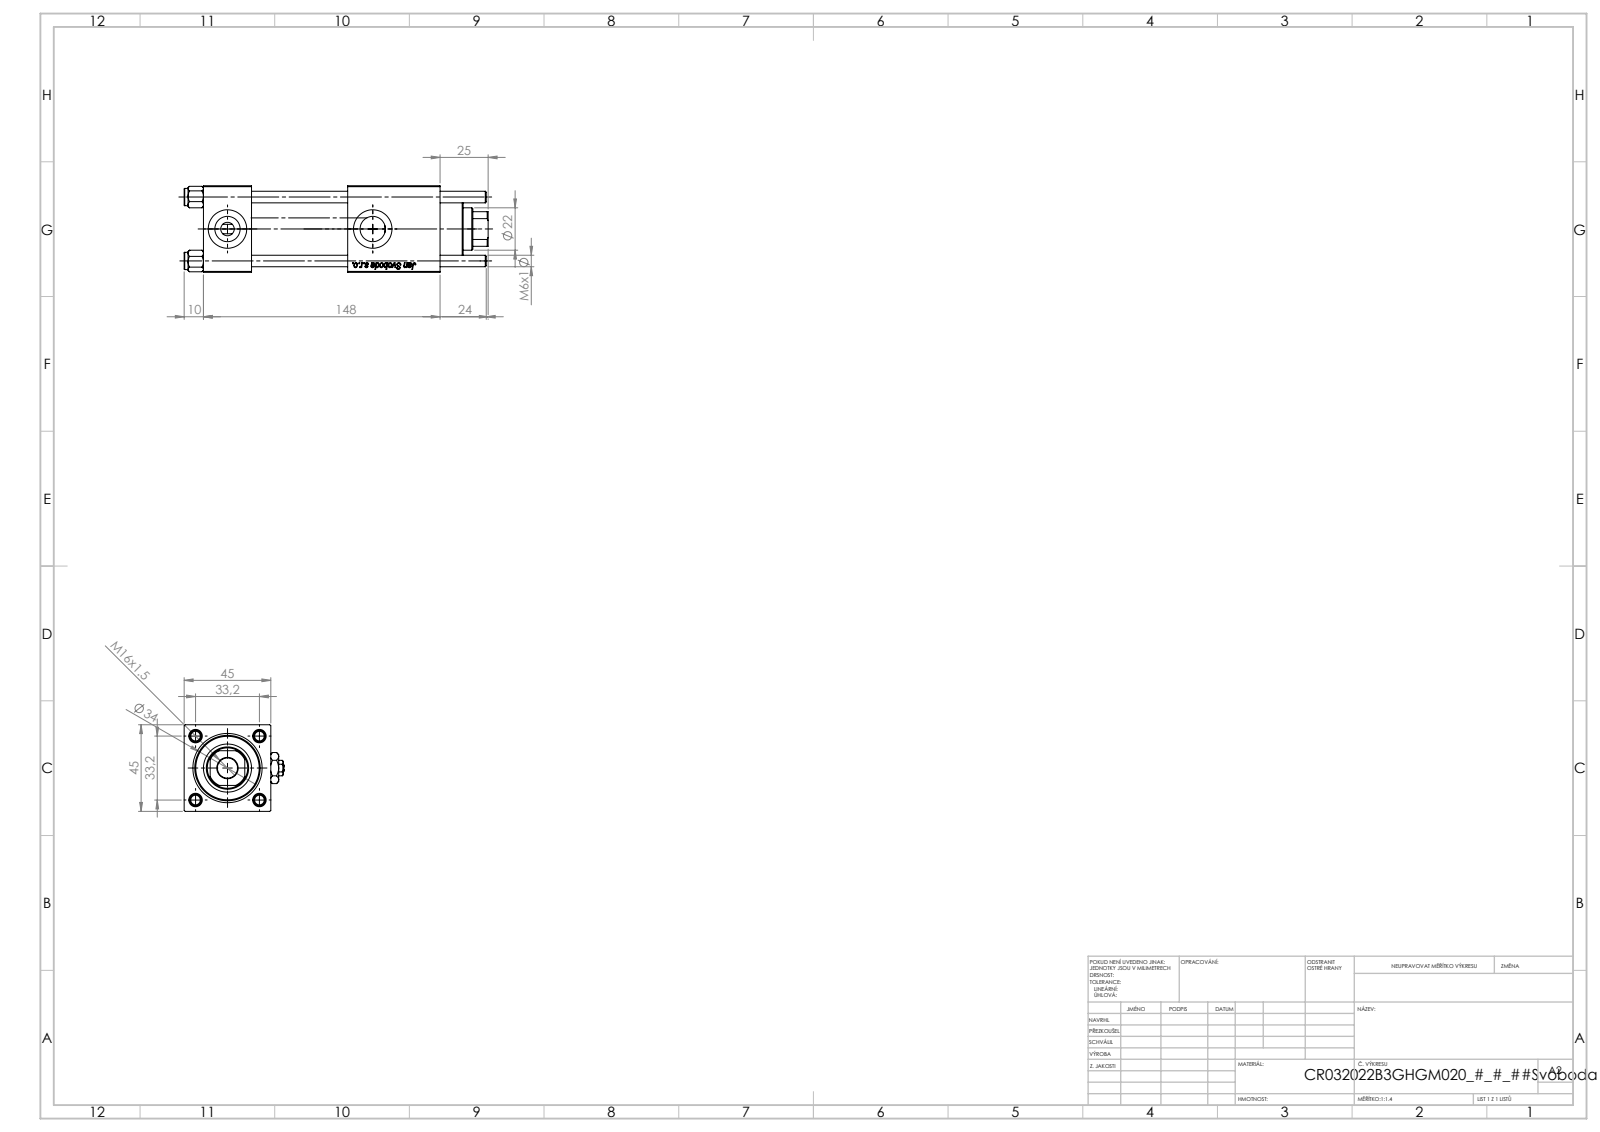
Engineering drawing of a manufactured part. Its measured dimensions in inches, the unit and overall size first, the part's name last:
Units: inches
Overall size (bounding box): 6.22 × 2.047 × 1.772
Round holes (diameter × count): ⌀0.236 ×4, ⌀0.276 ×2, ⌀0.518 ×2, ⌀0.787 ×2, ⌀0.413 ×1, ⌀0.866 ×1, ⌀0.945 ×1, ⌀0.984 ×1, ⌀1.26 ×1, ⌀1.299 ×1
Round bosses / shafts (diameter × count): ⌀0.354 ×4, ⌀1.496 ×1, ⌀1.339 ×1
Partial cylindrical surfaces — rounded edges, fillets, slot ends (radius × count): R0.413 ×1
Main face-to-face distances: 1.772, 0.984, 1.969, 4.843, 2.953, 1.764, 3.858, 1.89, 3.713, 2.728
Hole centre spacings: 0.924, 1.307, 1.848, 2.972
Volume: 12.98 in³ · Surface area: 121.9 in²
Bodies: 13 solids, 1256 faces (478 planar, 88 cylindrical, 690 other)
Part name (STEP PRODUCT): V215CR_B-1; NUT_M5_B; Zatka_pro_OIL_PORT; V215CR_VCP_B (+2 more)
STEP written by: SolidWorks 2019 (CONFIG_CONTROL_DESIGN)
